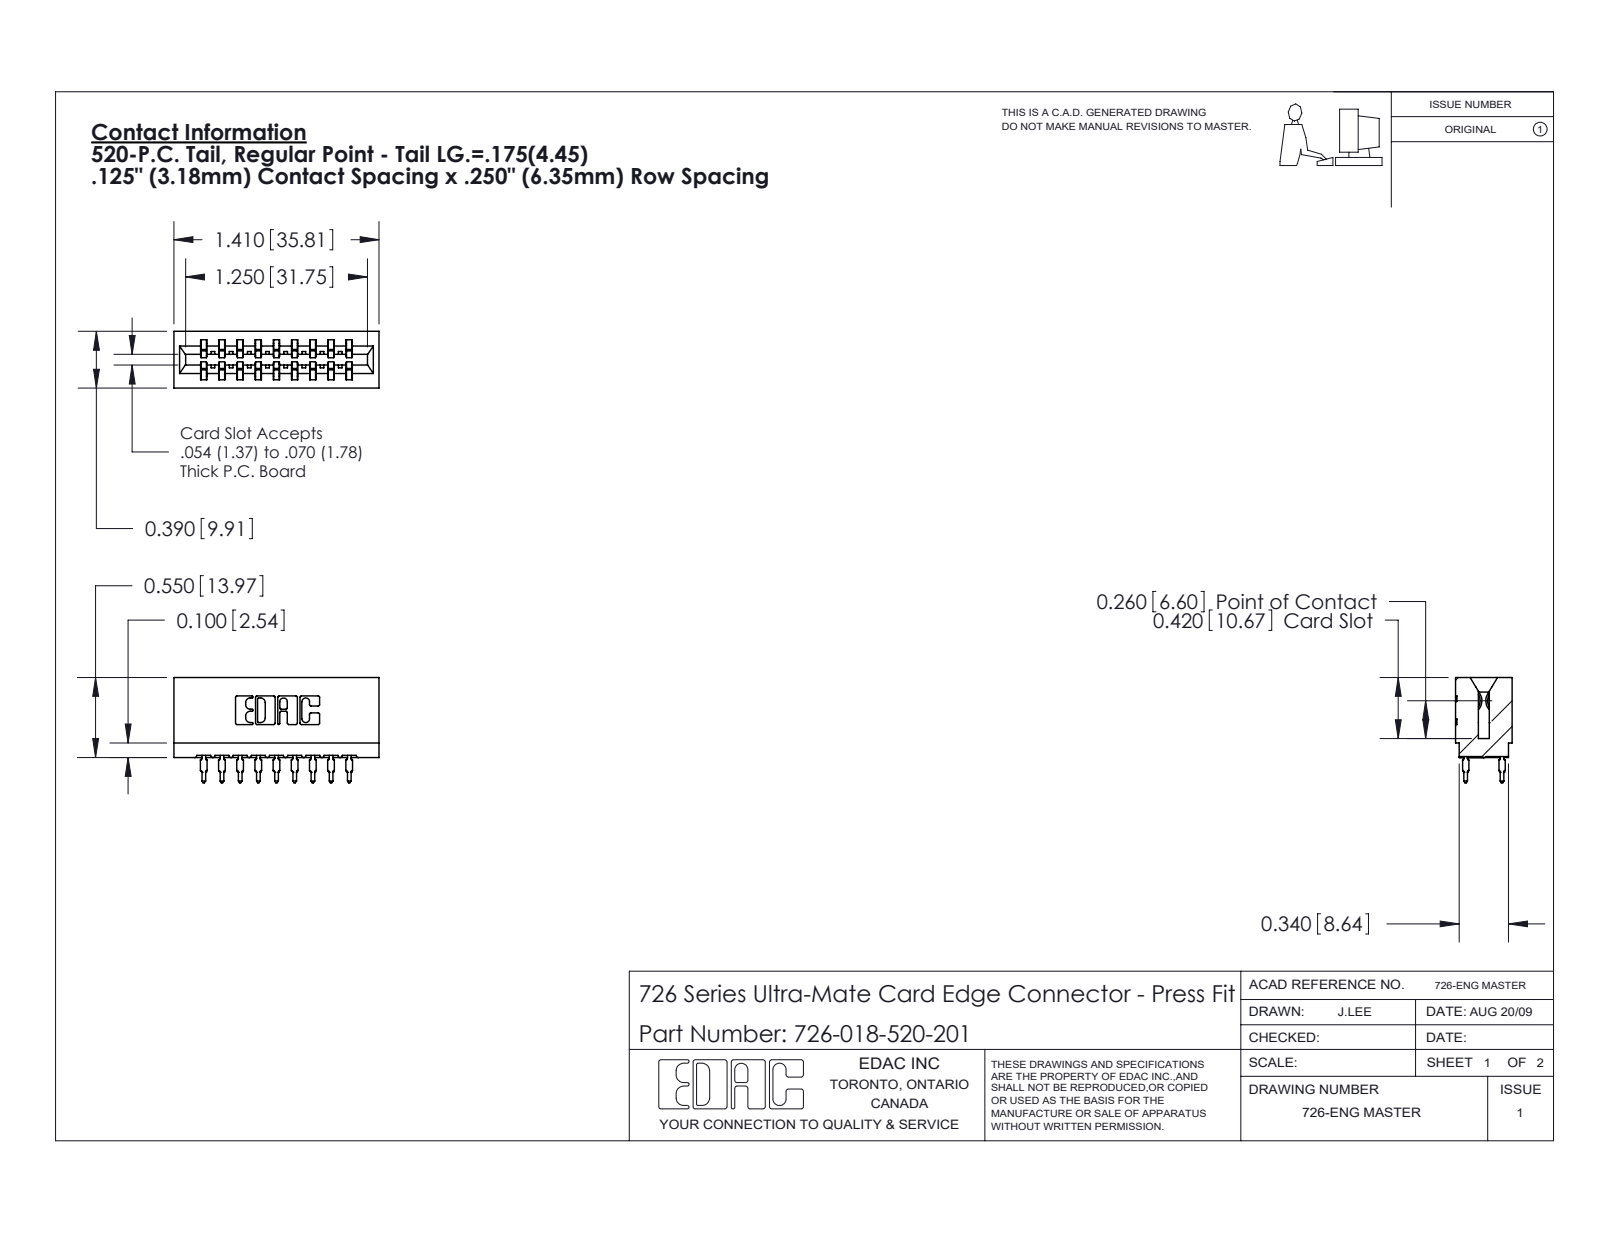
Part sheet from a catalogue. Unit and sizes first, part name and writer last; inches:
Units: inches
Overall size (bounding box): 1.41 × 0.724 × 0.39
Partial cylindrical surfaces — rounded edges, fillets, slot ends (radius × count): R0.021 ×36, R0.01 ×22, R0.015 ×10, R0.005 ×8, R0.011 ×8, R0.007 ×6, R0.031 ×6, R0.026 ×3
Main face-to-face distances: 0.25, 0.5, 0.333, 0.042, 0.057, 0.125, 0.125, 0.208, 0.292, 0.083
Volume: 0.211 in³ · Surface area: 7.896 in²
Bodies: 19 solids, 1708 faces (883 planar, 357 cylindrical, 468 other)
Part name (STEP PRODUCT): 726 Part_.515 Slot Depth - 01; 746-292-001_520; 726-018-520-201
STEP written by: SolidWorks 2020 (CONFIG_CONTROL_DESIGN)
